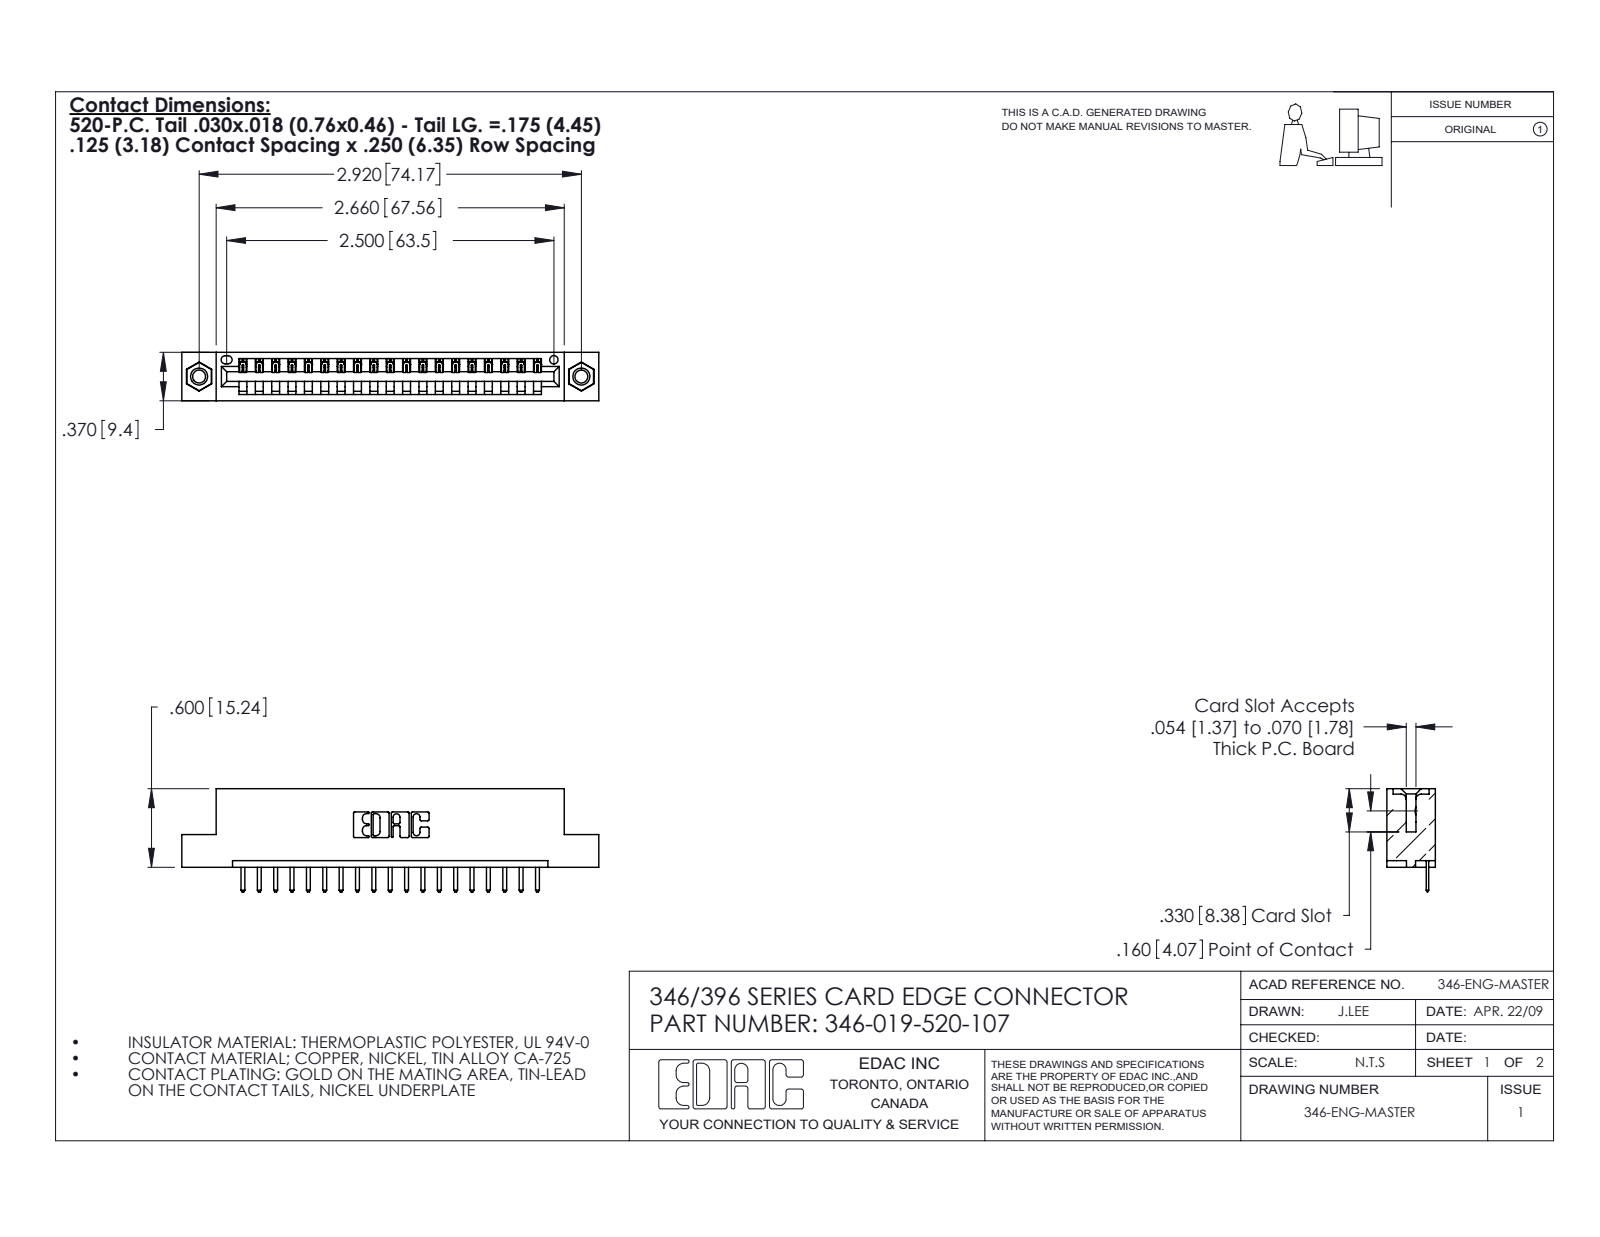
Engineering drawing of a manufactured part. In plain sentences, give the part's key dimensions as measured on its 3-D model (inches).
The part is named "346 Part_Flush Mounting Lugs - 0.156 Dia-TI; 345-250-001_345-250-005-103; 346-019-520-107; 345-292-001_345-293-120". Its 3-D file was written by "SolidWorks 2020 (CONFIG_CONTROL_DESIGN)". It is 22 solids with 1360 faces: 906 planar, 438 cylindrical and 16 other. Overall it measures 3.185 by 0.788 by 0.37 inches. Its volume is 0.459 cubic inches and its surface area 13.95 square inches. Round holes: 2 of diameter 0.098, 2 of diameter 0.125, 2 of diameter 0.156, 1 of diameter 0.064. Round bosses or shafts: 2 of diameter 0.155. Partial cylindrical surfaces (rounded edges, fillets, slot ends): 40 of radius 0.01, 38 of radius 0.006, 22 of radius 0.01, 6 of radius 0.007, 6 of radius 0.031, 3 of radius 0.026, 2 of radius 0.031, 2 of radius 0.04. The main face-to-face distances are 0.048, 0.322, 0.37, 0.25, 0.148, 0.222, 0.1, 0.174, 0.072, 0.298. The hole center spacings are 0.246, 2.713, 2.92.
